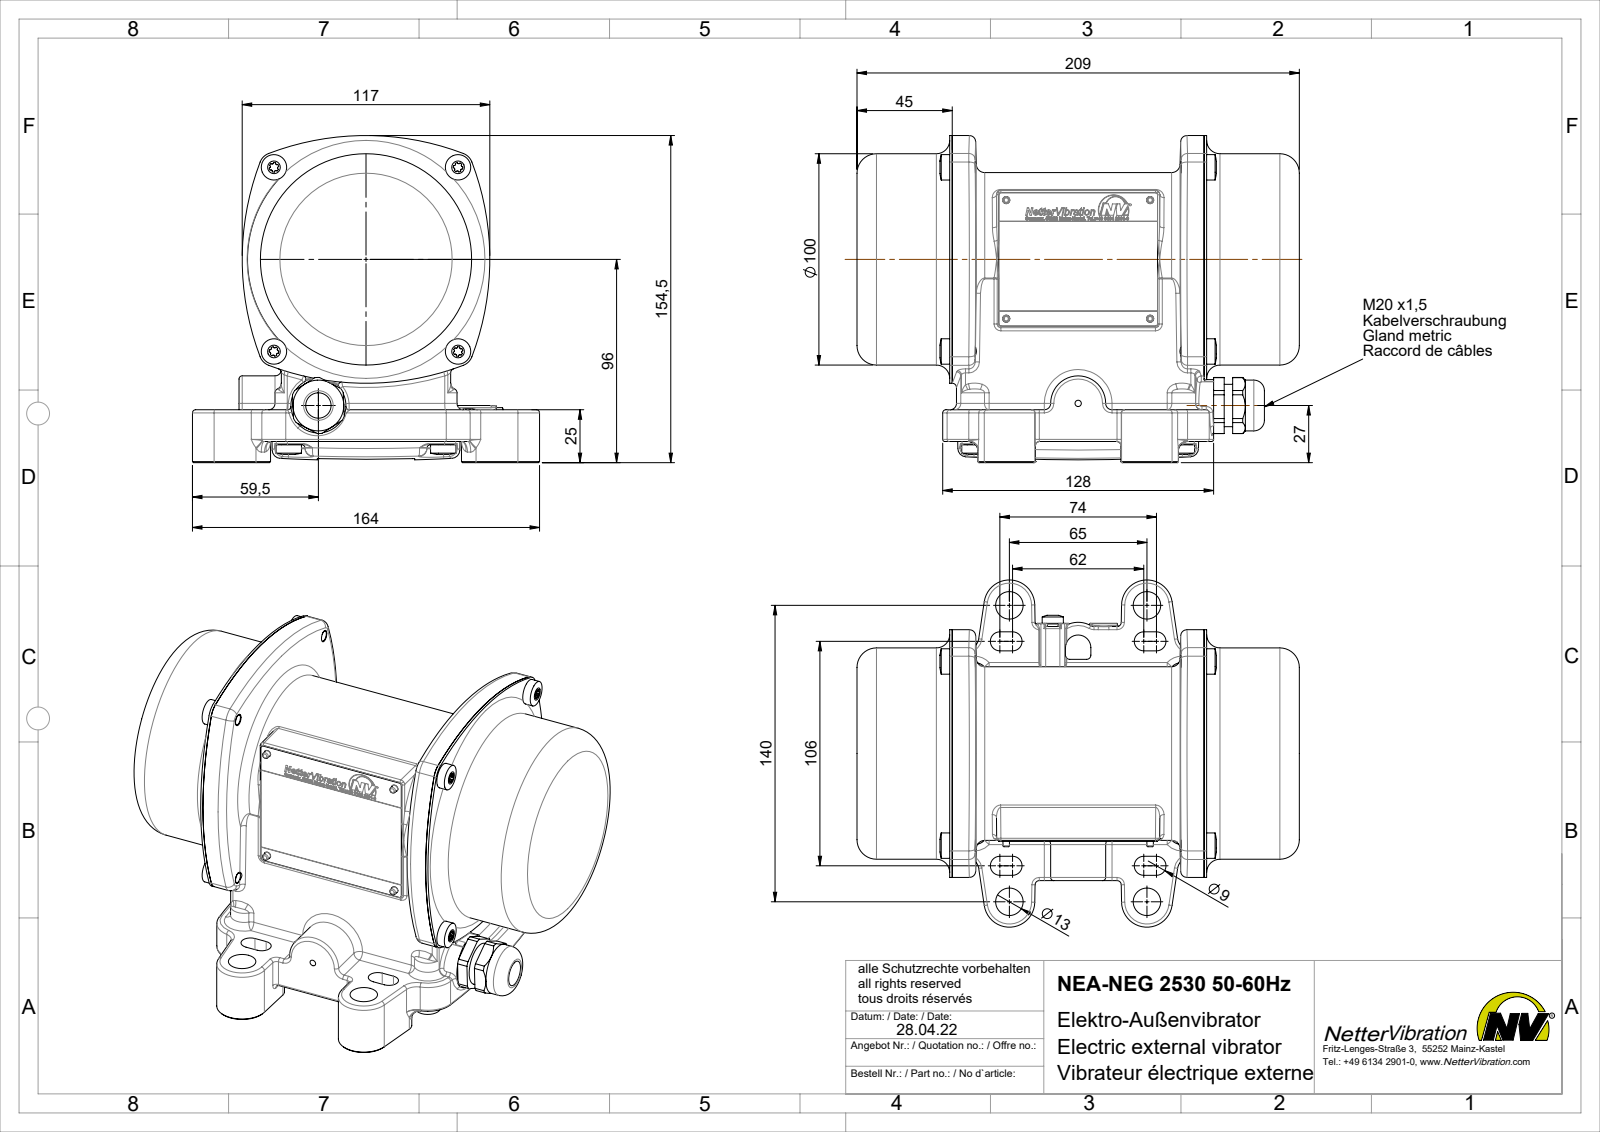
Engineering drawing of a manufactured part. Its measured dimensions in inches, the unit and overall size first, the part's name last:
Units: inches
Overall size (bounding box): 8.228 × 6.457 × 6.083
Round holes (diameter × count): ⌀0.134 ×4, ⌀0.276 ×4, ⌀0.413 ×1, ⌀0.453 ×1, ⌀0.472 ×1, ⌀0.512 ×1, ⌀0.571 ×1, ⌀0.728 ×1, ⌀3.307 ×1, ⌀3.835 ×1
Round bosses / shafts (diameter × count): ⌀0.472 ×8, ⌀0.236 ×8, ⌀3.929 ×1, ⌀0.945 ×1, ⌀0.787 ×1, ⌀0.512 ×1, ⌀0.394 ×1, ⌀0.197 ×1
Partial cylindrical surfaces — rounded edges, fillets, slot ends (radius × count): R0.02 ×79, R0.059 ×59, R0.008 ×41, R0.079 ×34, R0.039 ×26, R0.118 ×16, R0.236 ×15, R0.315 ×12
Main face-to-face distances: 0.047, 1.724, 6.457, 8.181, 1.772, 6.409, 0.787, 0.354, 0.079, 0.02
Hole centre spacings: 2.421, 3.424, 2.205, 2.677, 3.468, 4.843, 0.955, 1.301
Volume: 47.76 in³ · Surface area: 542.2 in²
Bodies: 22 solids, 3054 faces (776 planar, 788 cylindrical, 1490 other)
Part name (STEP PRODUCT): NEA-NEG 2530-50-60Hz
STEP written by: SolidWorks 2015 (AUTOMOTIVE_DESIGN)
